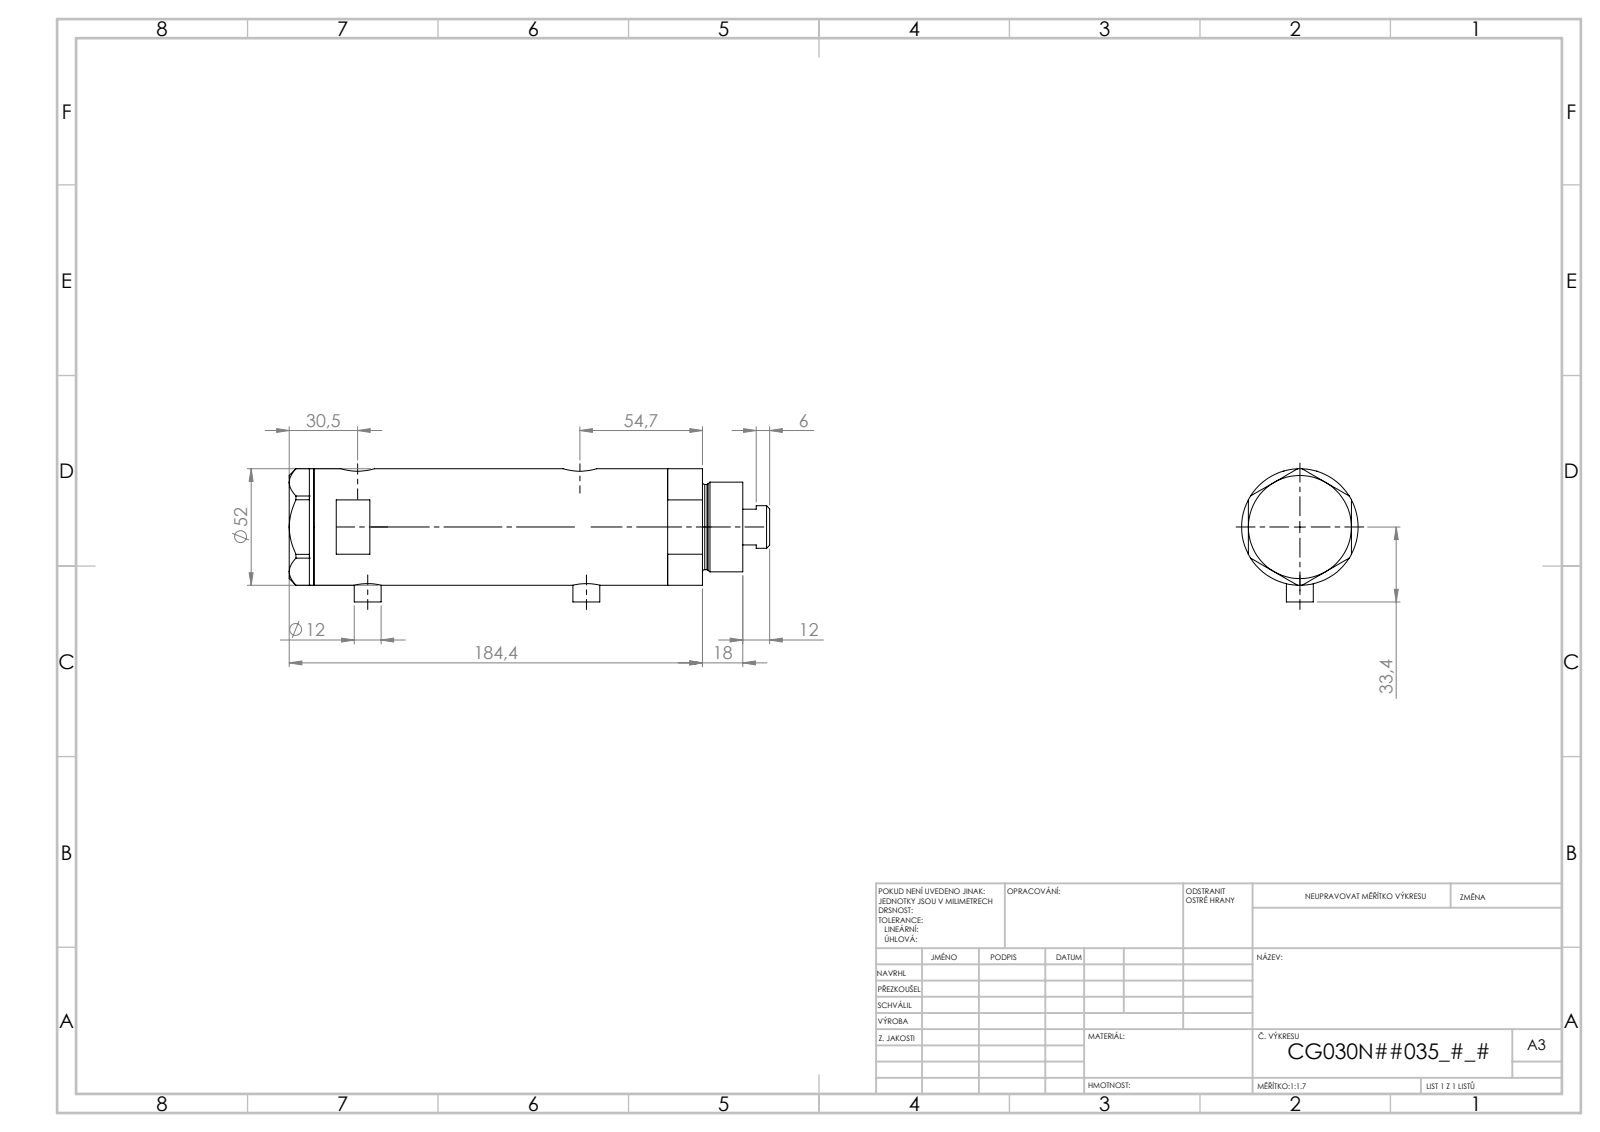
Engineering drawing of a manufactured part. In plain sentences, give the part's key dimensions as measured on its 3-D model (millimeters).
The part is named "V270CG_BACK; V270CG_MIDDLE; V270CG_FRONT; V270CG_VC". Its 3-D file was written by "SolidWorks 2019 (CONFIG_CONTROL_DESIGN)". It is 4 solids with 140 faces: 67 planar, 53 cylindrical and 20 other. Overall it measures 184.02 by 53.1 by 52 millimeters. Its volume is 328 104 cubic millimeters and its surface area 76 305 square millimeters. Round holes: 2 of diameter 5, 2 of diameter 9.73, 2 of diameter 12.5, 2 of diameter 15, 1 of diameter 6.5, 1 of diameter 20, 1 of diameter 21.5, 1 of diameter 30, 1 of diameter 33, 1 of diameter 44. Round bosses or shafts: 2 of diameter 12, 1 of diameter 52, 1 of diameter 40, 1 of diameter 38, 1 of diameter 19. The main face-to-face distances are 23.8, 11, 34.8, 46, 99.56, 88.56, 64.76, 135.96, 124.96, 101.16. The hole center spacings are 2.9, 4.5, 61.75, 64.65, 66.25, 69.15, 2.89, 2.91.
